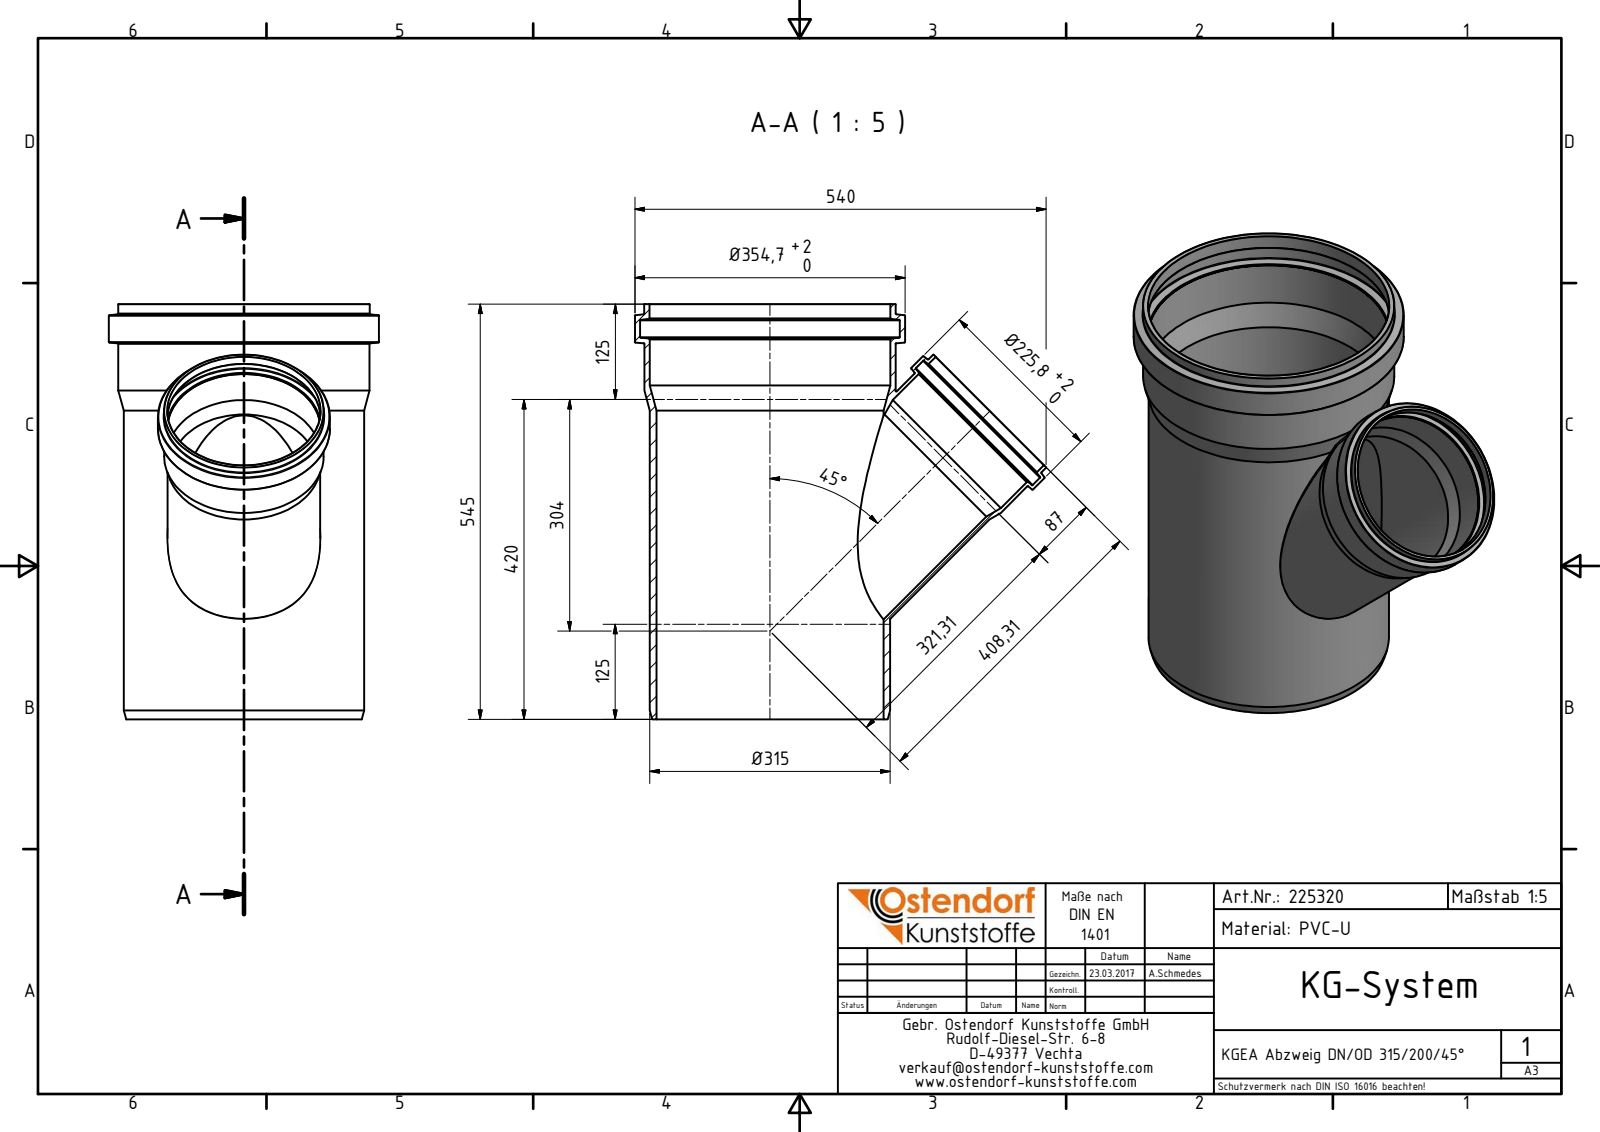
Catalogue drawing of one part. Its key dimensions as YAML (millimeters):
part_name: "225320 KGEA Abzweig DN_OD 315_200_45°"
step_written_by: "Autodesk Inventor 2016 (AUTOMOTIVE_DESIGN)"
units: millimeters
bodies: {solids: 1, faces: 62, planar: 5, cylindrical: 18, other: 39}
overall_size: [545, 540, 354.7]
volume: 4929000
surface_area: 1327000
round_holes:
  - {diameter: 200.9, count: 2}
  - {diameter: 189.3, count: 1}
  - {diameter: 200.6, count: 1}
  - {diameter: 217, count: 1}
  - {diameter: 298.2, count: 1}
  - {diameter: 316, count: 1}
  - {diameter: 316.3, count: 1}
  - {diameter: 340.9, count: 1}
round_bosses_or_shafts:
  - {diameter: 354.7, count: 1}
  - {diameter: 330.1, count: 1}
  - {diameter: 329.8, count: 1}
  - {diameter: 315.6, count: 1}
  - {diameter: 225.8, count: 1}
  - {diameter: 209.7, count: 1}
  - {diameter: 209.4, count: 1}
  - {diameter: 200.5, count: 1}
face_to_face_distances: [545, 498.44, 46.56, 31.76]
